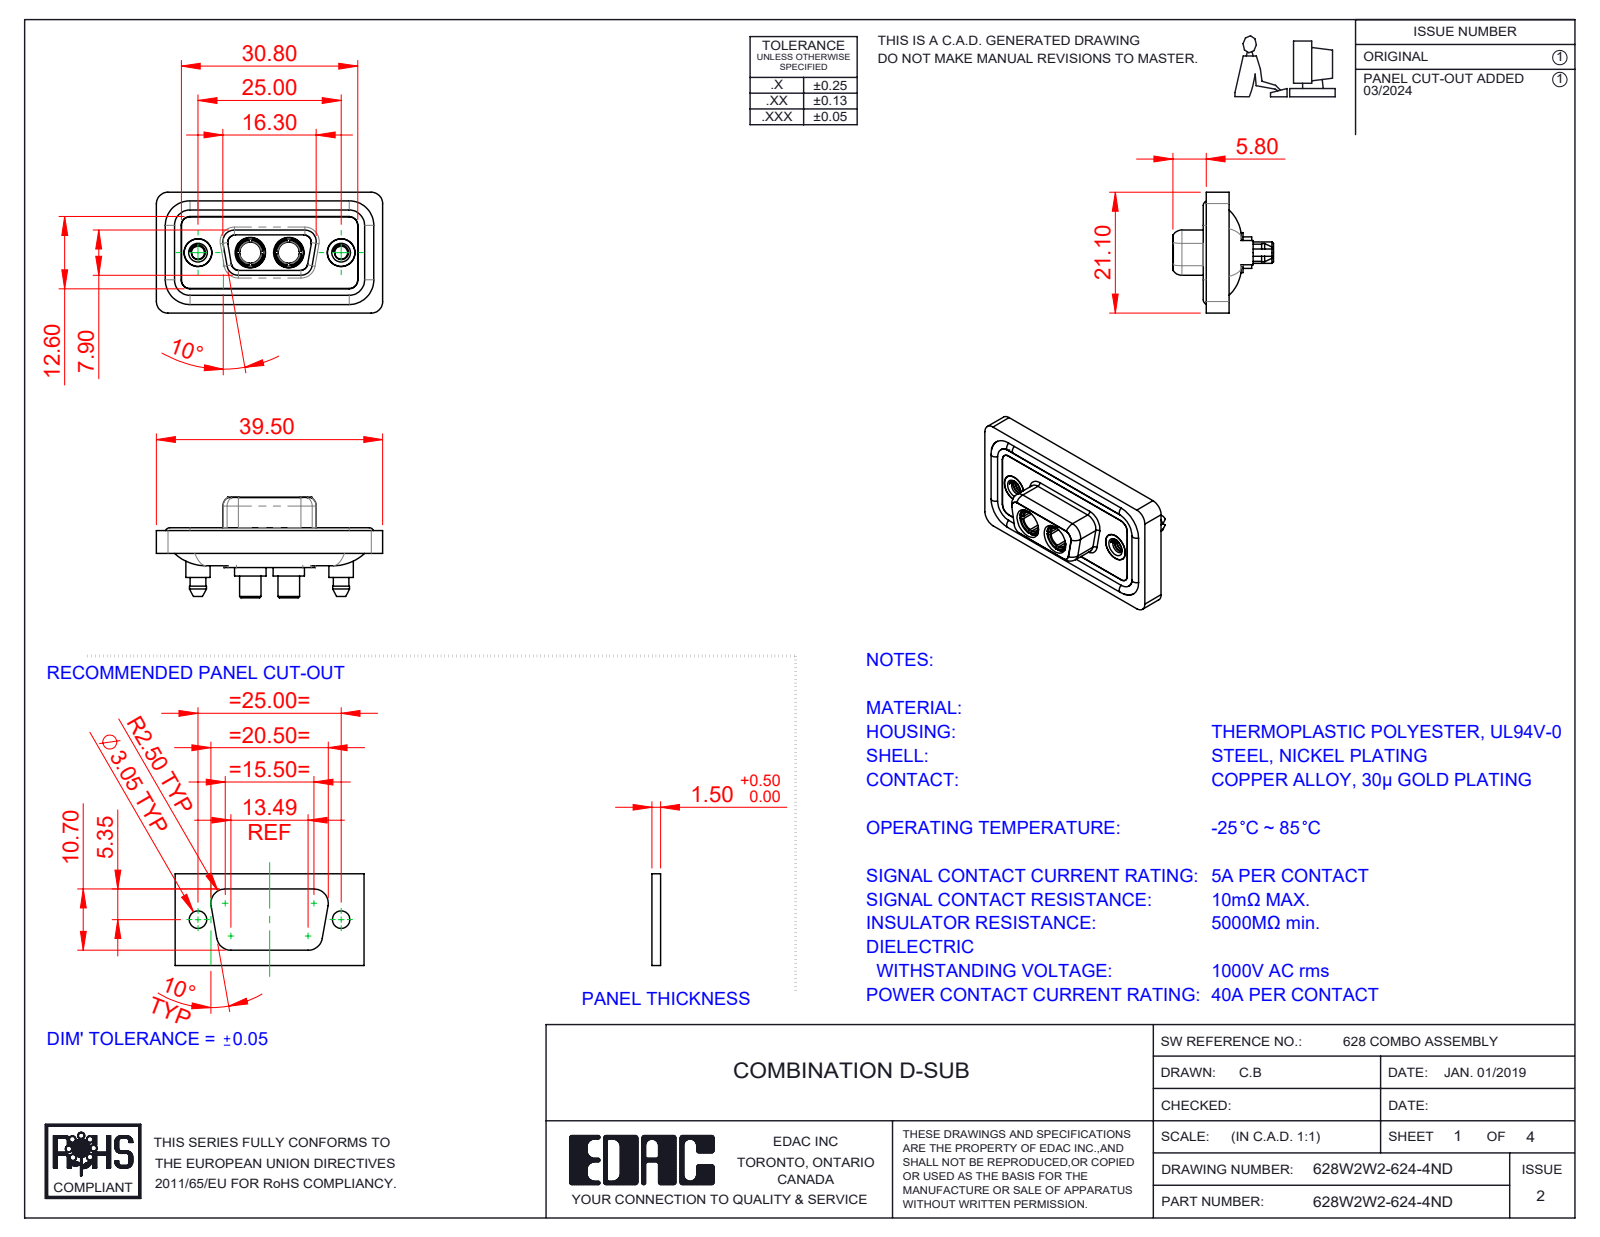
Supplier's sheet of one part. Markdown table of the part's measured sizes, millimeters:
| quantity | value |
| --- | --- |
| part name | Power Socket_40A S; 628Combo Housing_2W2; 628W2W2-624-4ND; 628Combo Shell Front_09 Contacts (+3 more) |
| STEP written by | SolidWorks 2023 (CONFIG_CONTROL_DESIGN) |
| units | millimeters |
| bodies | 11 solids, 600 faces (179 planar, 282 cylindrical, 139 other) |
| overall size | 39.5 × 21.1 × 17.55 |
| volume | 4 885 mm³ |
| surface area | 7 997 mm² |
| round holes (diameter × count) | 4.85 × 4, 2.26 × 2, 3.7 × 2, 4 × 2, 4.05 × 2, 5 × 2, 5.3 × 2 |
| round bosses / shafts (diameter × count) | 1.6 × 4, 5.5 × 2, 5.4 × 2, 5.2 × 2, 4.96 × 2, 4.95 × 2, 4.8 × 2, 4.75 × 2 |
| partial cylindrical surfaces (radius × count) | 1.5 × 24, 2 × 18, 1.6 × 10, 1.35 × 8, 0.25 × 4, 0.5 × 4, 0.6 × 4, 0.65 × 4 |
| main face-to-face distances | 0.4, 1.8, 1.1, 2.9, 1.6, 0.5, 5.65, 7.45, 4, 1.5 |
| hole center spacings | 9.14, 15.86, 6.72, 25 |
